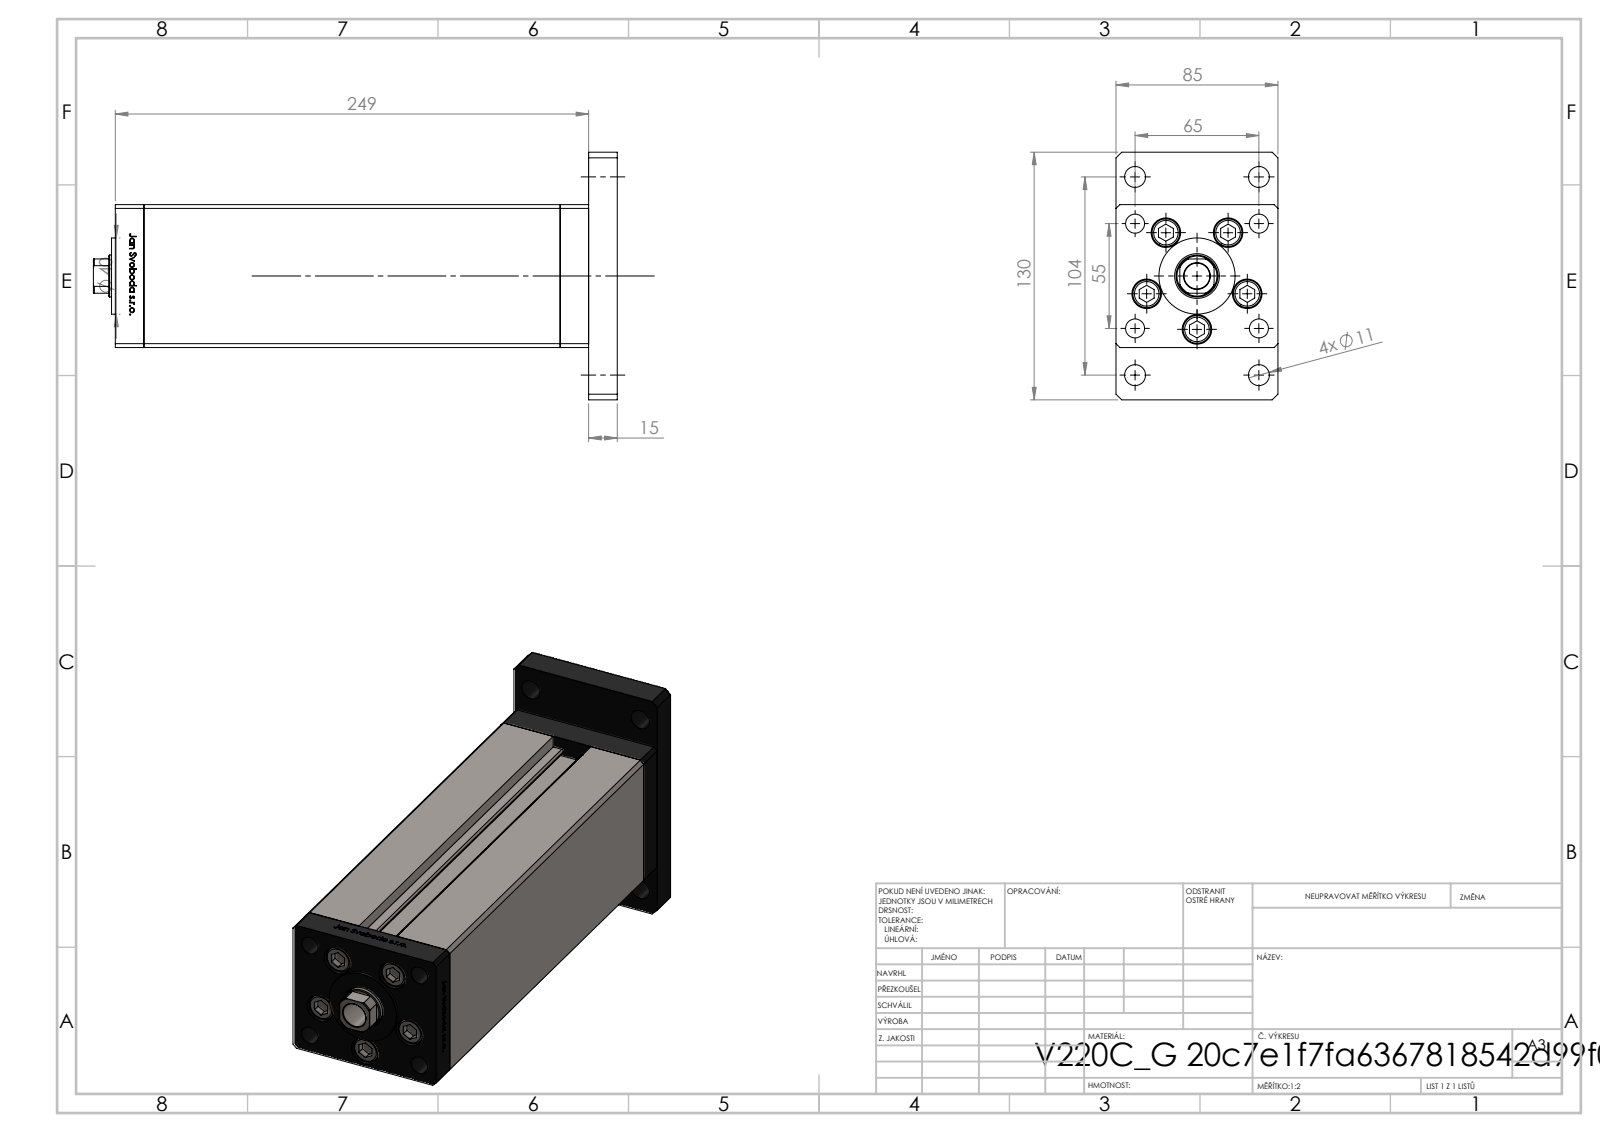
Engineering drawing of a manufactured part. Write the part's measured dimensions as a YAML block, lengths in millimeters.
part_name: "V220C_F; V220C_FRONT_G; V220C BACK_G; V220C_VC_G (+2 more)"
step_written_by: "SolidWorks 2019 (CONFIG_CONTROL_DESIGN)"
units: millimeters
bodies: {solids: 19, faces: 1301, planar: 514, cylindrical: 181, other: 606}
overall_size: [275, 130, 85]
volume: 1533000
surface_area: 233704
round_holes:
  - {diameter: 10, count: 9}
  - {diameter: 11, count: 9}
  - {diameter: 15.5, count: 5}
  - {diameter: 14.5, count: 4}
  - {diameter: 13.5, count: 1}
  - {diameter: 22, count: 1}
  - {diameter: 23.5, count: 1}
  - {diameter: 56, count: 1}
round_bosses_or_shafts:
  - {diameter: 8, count: 9}
  - {diameter: 14.5, count: 5}
  - {diameter: 40, count: 1}
partial_cylinders:
  - {radius: 0.93, count: 2}
  - {radius: 10.5, count: 1}
face_to_face_distances: [15, 85, 75, 233.5, 248.5, 218.5, 30, 2, 246.5, 263.5]
hole_center_spacings: [28, 24.5, 42.57, 61.32, 65, 69.46, 79.5, 102.69]
